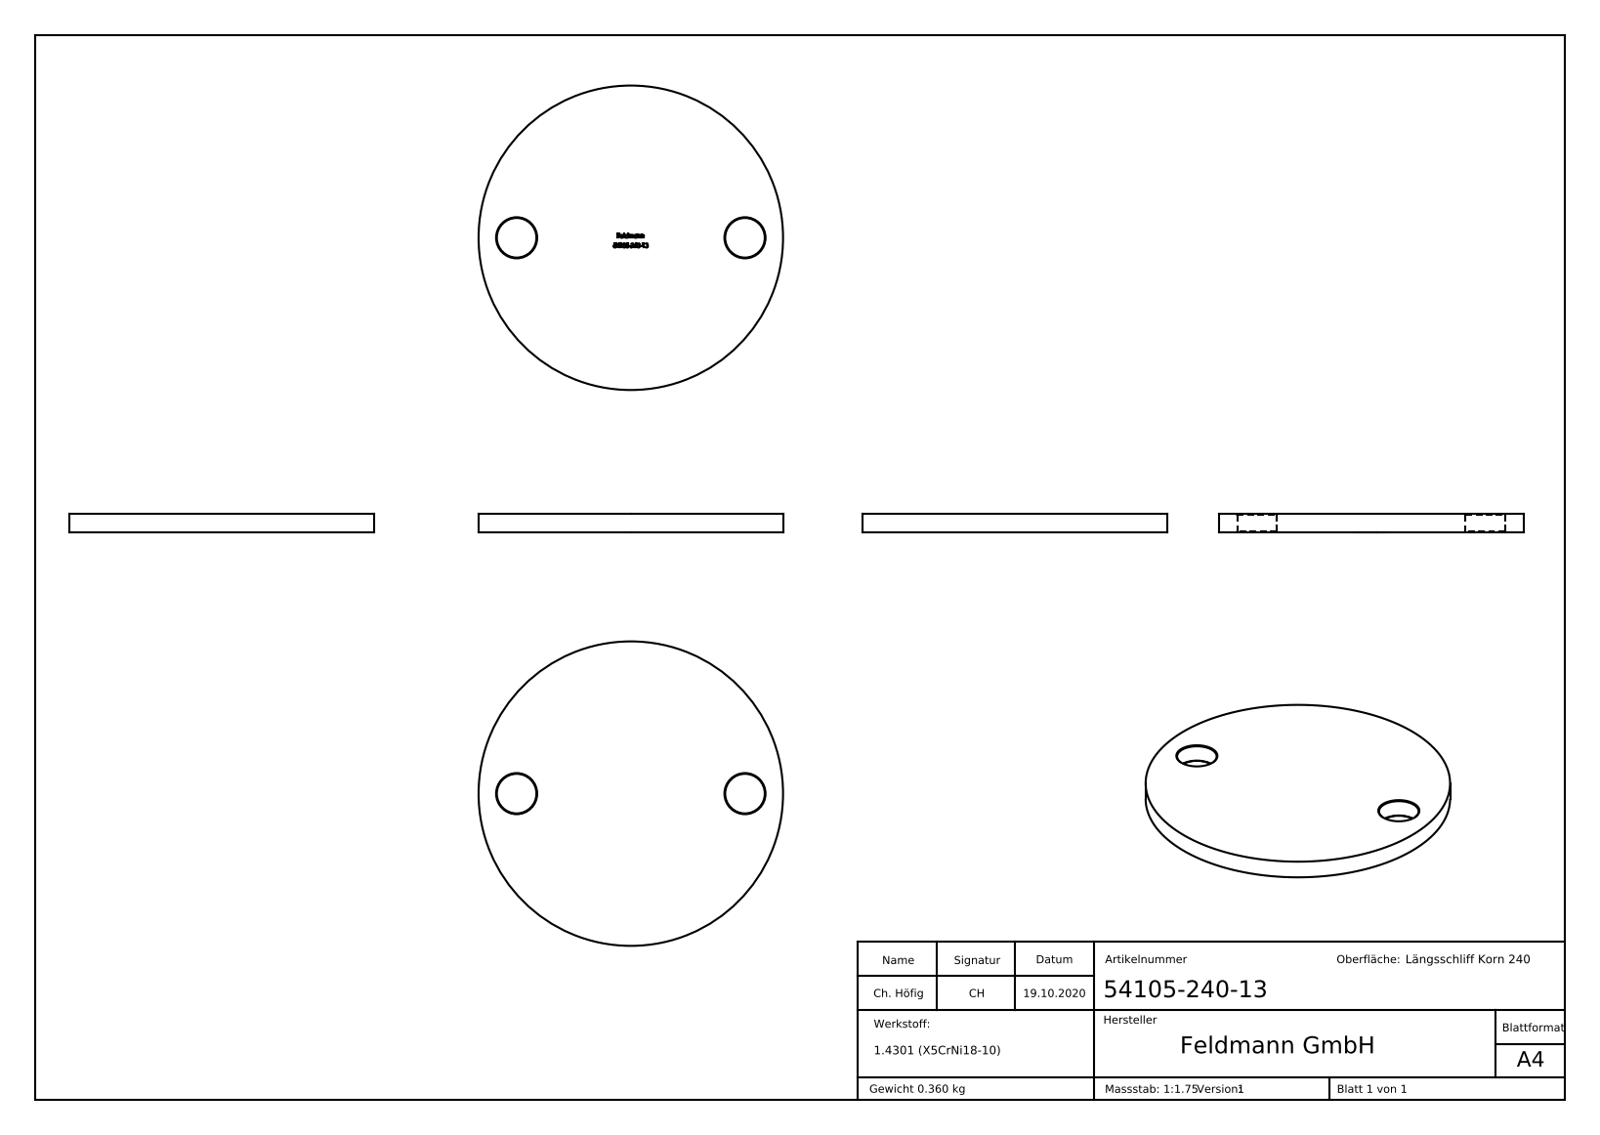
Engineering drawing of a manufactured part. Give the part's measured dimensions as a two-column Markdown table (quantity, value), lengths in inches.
| quantity | value |
| --- | --- |
| part name | 54105-240-13 |
| STEP written by | SolidWorks 2018 (CONFIG_CONTROL_DESIGN) |
| units | inches |
| bodies | 1 solid, 266 faces (150 planar, 6 cylindrical, 110 other) |
| overall size | 3.937 × 3.937 × 0.236 |
| volume | 2.778 in³ |
| surface area | 27.19 in² |
| round holes (diameter × count) | 0.512 × 2 |
| round bosses / shafts (diameter × count) | 3.937 × 1 |
| main face-to-face distances | 0.236, 0.232, 0.047, 0.091, 0.087, 0.126, 0.289, 0.102, 0.117, 0.16 |
| hole center spacings | 2.953 |
